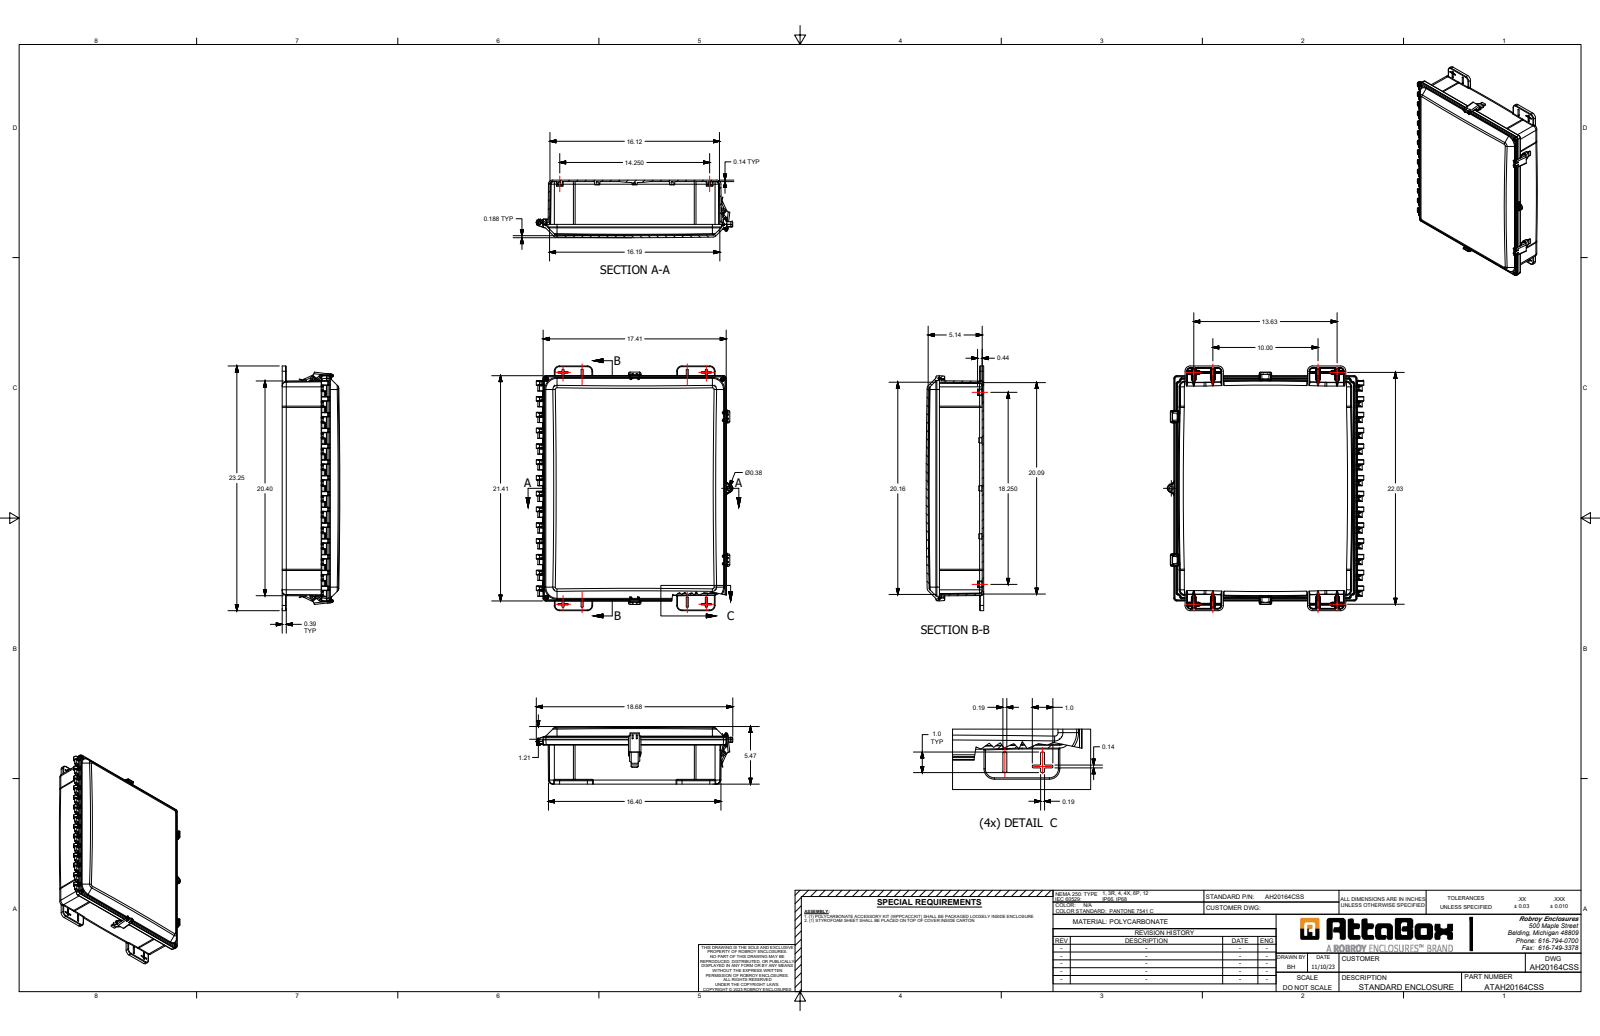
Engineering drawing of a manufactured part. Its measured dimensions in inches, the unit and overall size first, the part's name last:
Units: inches
Overall size (bounding box): 23.25 × 18.676 × 5.473
Round holes (diameter × count): ⌀0.187 ×21, ⌀0.195 ×4, ⌀0.25 ×4, ⌀0.296 ×4, ⌀0.39 ×4, ⌀0.14 ×3, ⌀0.209 ×3, ⌀0.327 ×1, ⌀0.375 ×1, ⌀0.45 ×1
Round bosses / shafts (diameter × count): ⌀0.487 ×21, ⌀0.625 ×4, ⌀0.24 ×3, ⌀0.199 ×3, ⌀0.15 ×3, ⌀0.12 ×3, ⌀0.313 ×1
Partial cylindrical surfaces — rounded edges, fillets, slot ends (radius × count): R0.035 ×84, R0.1 ×25, R0.039 ×24, R0.065 ×18, R0.05 ×16, R0.15 ×16, R0.02 ×10, R0.059 ×8
Main face-to-face distances: 0.14, 4.205, 4.065, 16.213, 20.21, 0.187, 0.5, 3.705, 3.565, 0.107
Hole centre spacings: 5.789, 9.796, 14.143, 3.563, 4.563, 8.461, 7.125, 8.461
Volume: 179.9 in³ · Surface area: 2 351 in²
Bodies: 18 solids, 1630 faces (766 planar, 538 cylindrical, 326 other)
Part name (STEP PRODUCT): AH20164SS
STEP written by: SolidWorks 2023 (AUTOMOTIVE_DESIGN)
